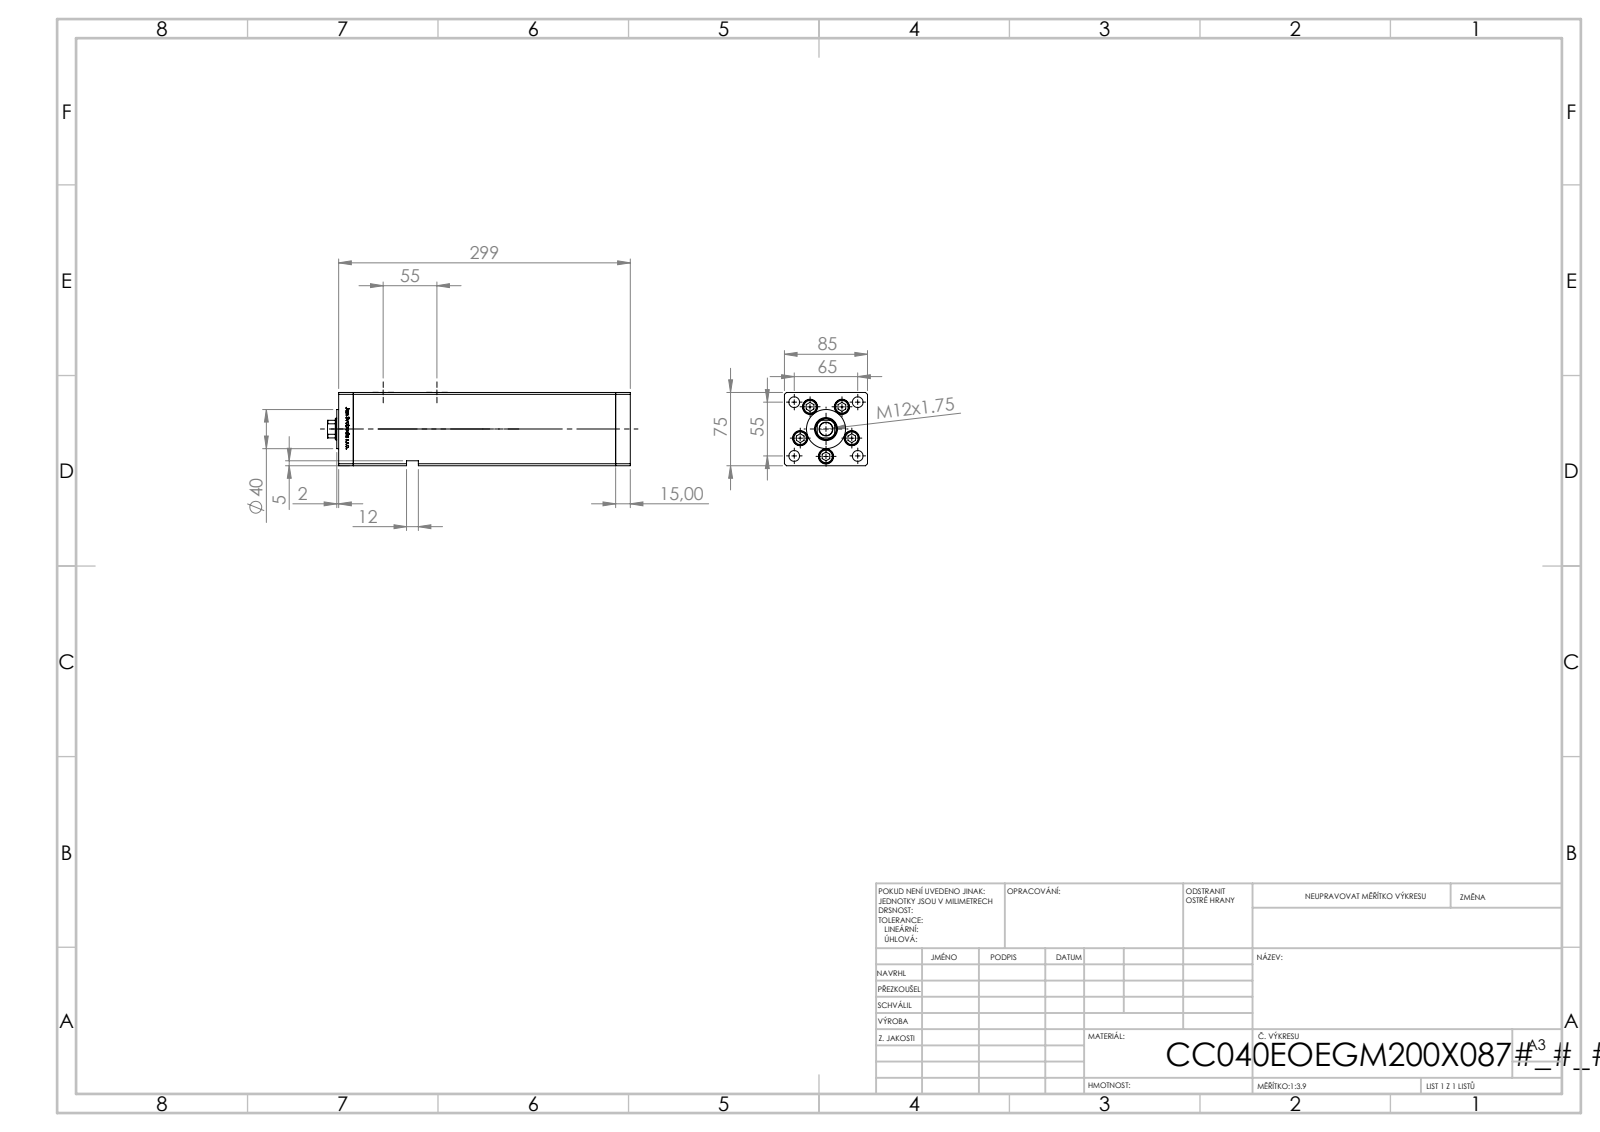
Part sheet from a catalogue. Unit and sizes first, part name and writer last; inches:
Units: inches
Overall size (bounding box): 12.205 × 3.346 × 2.953
Round holes (diameter × count): ⌀0.433 ×9, ⌀0.61 ×5, ⌀0.413 ×4, ⌀0.65 ×4, ⌀0.079 ×2, ⌀0.518 ×2, ⌀0.531 ×1, ⌀0.866 ×1, ⌀0.925 ×1
Round bosses / shafts (diameter × count): ⌀0.571 ×5, ⌀0.315 ×5, ⌀1.575 ×1
Partial cylindrical surfaces — rounded edges, fillets, slot ends (radius × count): R0.037 ×2, R0.413 ×1
Main face-to-face distances: 3.346, 2.953, 0.591, 10.571, 11.161, 0.413, 2.697, 11.752, 2.539, 1.23
Hole centre spacings: 1.102, 1.676, 2.165, 2.559, 3.352, 0.664, 0.755, 1.273
Volume: 98 in³ · Surface area: 366.3 in²
Bodies: 14 solids, 1214 faces (475 planar, 165 cylindrical, 574 other)
Part name (STEP PRODUCT): V220C_FRONT_E; V220C BACK_E; V220C_E MIDDLE; ALLEN BOLT (+1 more)
STEP written by: SolidWorks 2019 (CONFIG_CONTROL_DESIGN)
